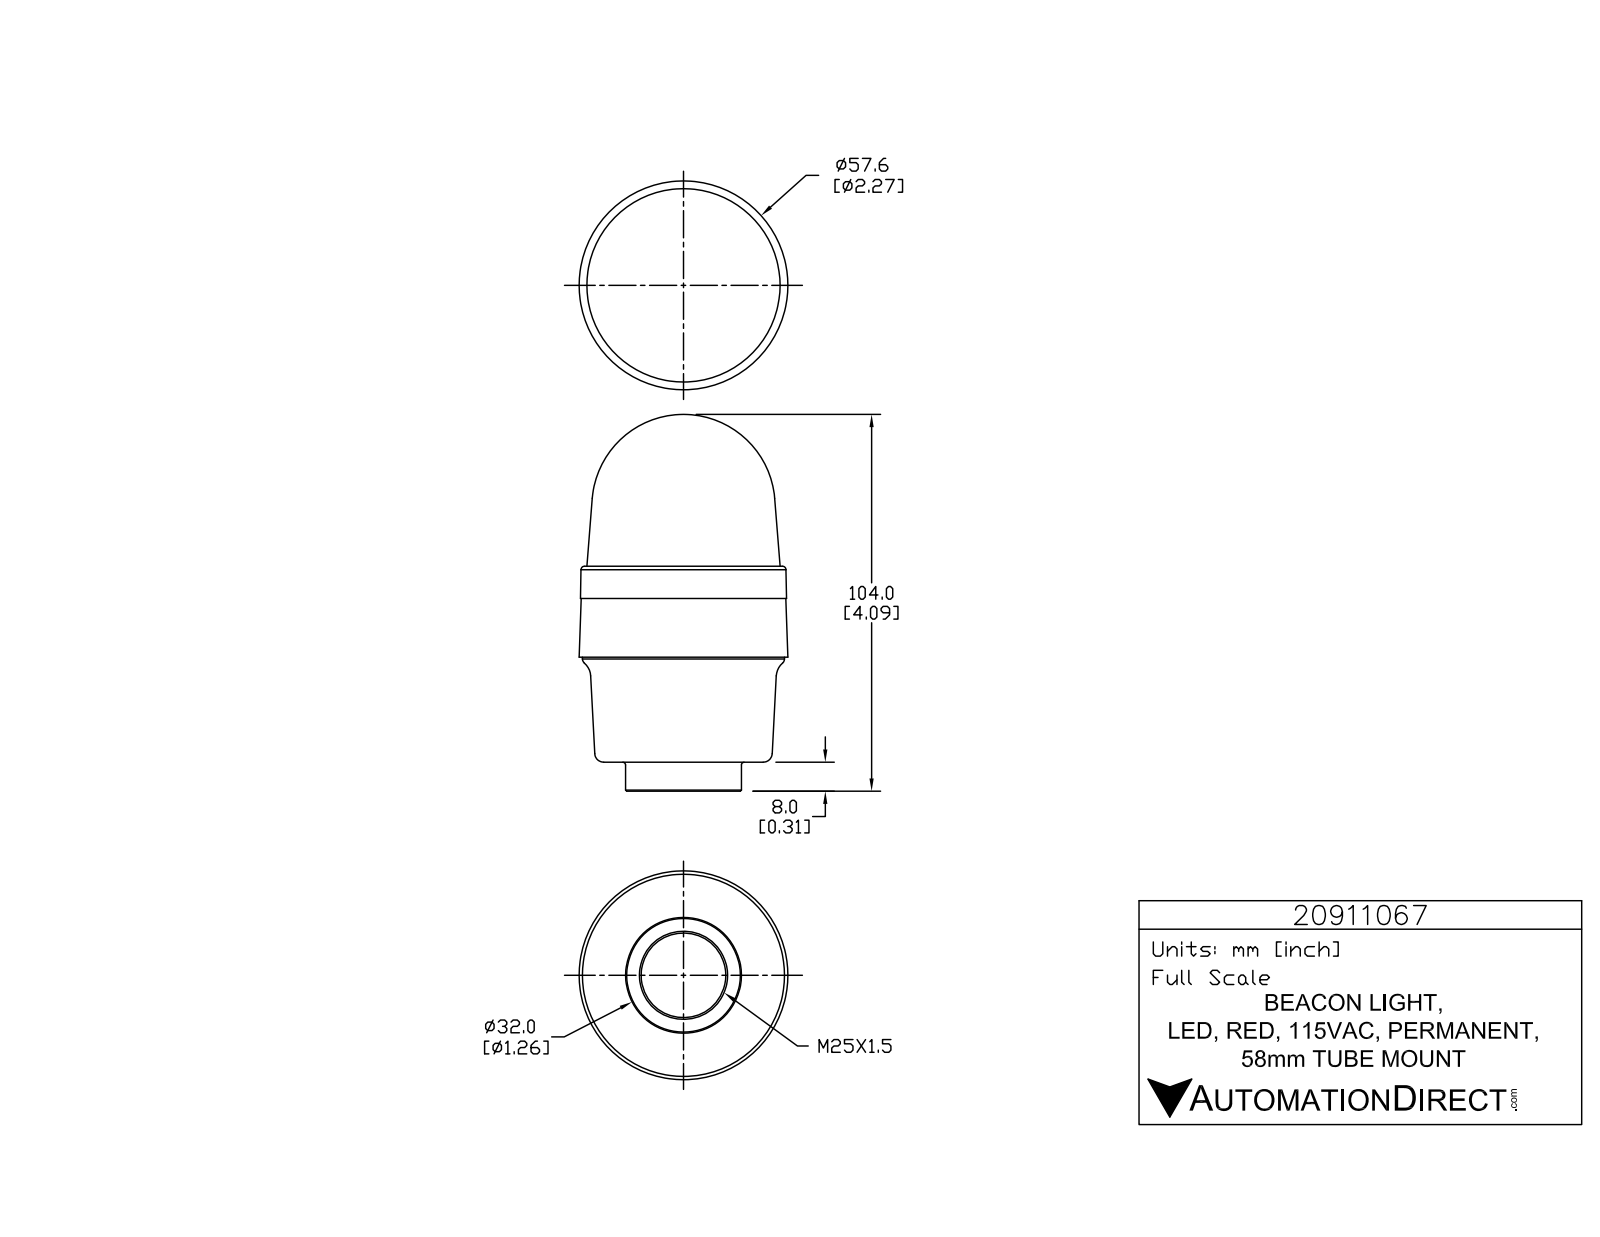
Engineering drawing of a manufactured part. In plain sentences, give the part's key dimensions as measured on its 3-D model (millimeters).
The part is named "20911067". Its 3-D file was written by "SolidWorks 2015 (AUTOMOTIVE_DESIGN)". It is 1 solid with 791 faces: 525 planar, 168 cylindrical and 98 other. Overall it measures 102.9 by 57.6 by 57.6 millimeters. Its volume is 192 100 cubic millimeters and its surface area 19 310 square millimeters. Round holes: 3 of diameter 1, 1 of diameter 23.4. Round bosses or shafts: 3 of diameter 5.7, 3 of diameter 1.4, 1 of diameter 55.8, 1 of diameter 32. Partial cylindrical surfaces (rounded edges, fillets, slot ends): 6 of radius 0.2, 6 of radius 0.2, 6 of radius 0.2, 6 of radius 3.3, 3 of radius 0.1, 3 of radius 0.1, 3 of radius 0.2, 3 of radius 0.2. The main face-to-face distances are 8, 29, 37, 25.1, 54.1, 62.1, 8.9, 16.2, 45.2, 53.2.
